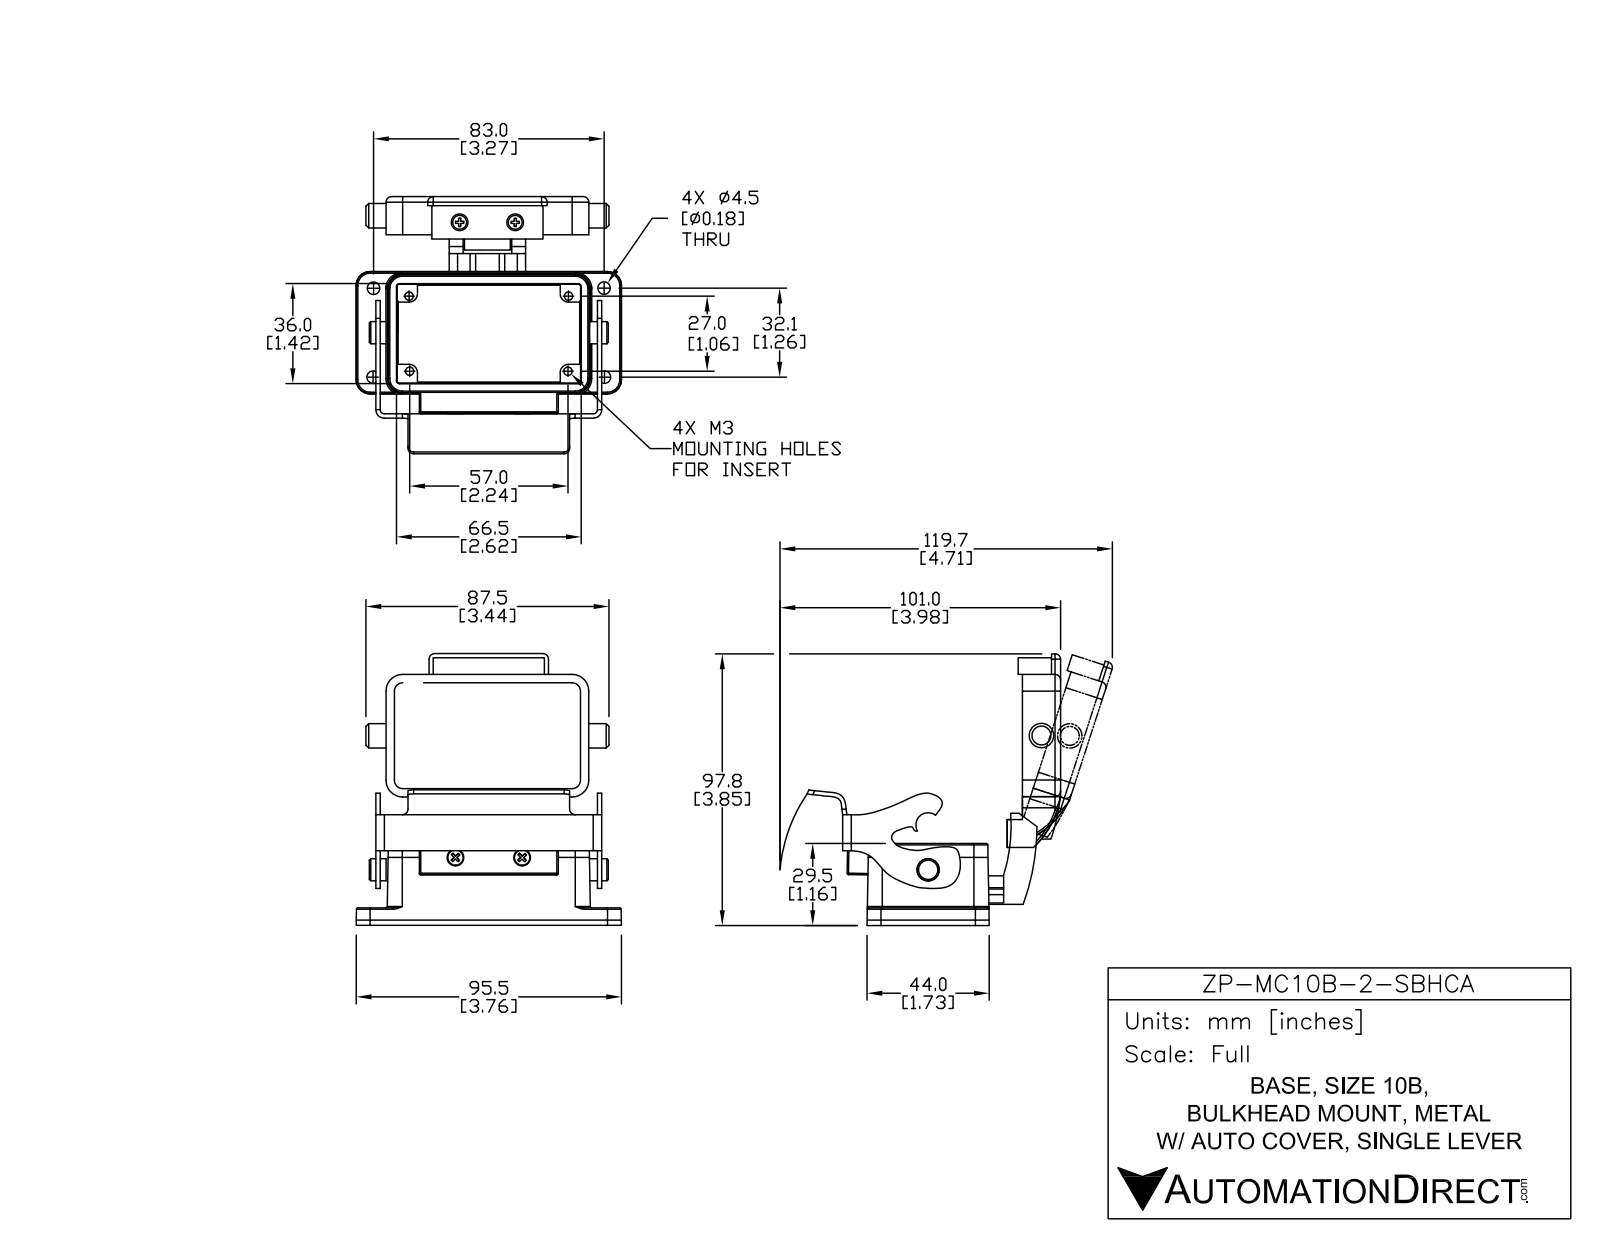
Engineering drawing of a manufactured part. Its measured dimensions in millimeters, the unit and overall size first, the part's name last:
Units: millimetres
Overall size (bounding box): 97.7 × 95.5 × 86.13
Round holes (diameter × count): ⌀3 ×4, ⌀4.5 ×4, ⌀2 ×1, ⌀8 ×1
Round bosses / shafts (diameter × count): ⌀8 ×1, ⌀7.95 ×1
Partial cylindrical surfaces — rounded edges, fillets, slot ends (radius × count): R0.5 ×29, R2 ×17, R5 ×6, R3 ×4, R1 ×3, R1.5 ×2, R3.06 ×2, R8 ×2
Main face-to-face distances: 3, 1.56, 39.49, 39.48, 69.4, 79.76, 7.51, 14, 11, 6.3
Hole centre spacings: 13.24, 32.24, 70.04, 75.96, 27, 32, 57, 63.07
Volume: 72 131 mm³ · Surface area: 44 404 mm²
Bodies: 4 solids, 428 faces (192 planar, 126 cylindrical, 110 other)
Part name (STEP PRODUCT): ZP-MC10B-2-SBHCA
STEP written by: SolidWorks 2014 (AUTOMOTIVE_DESIGN)
